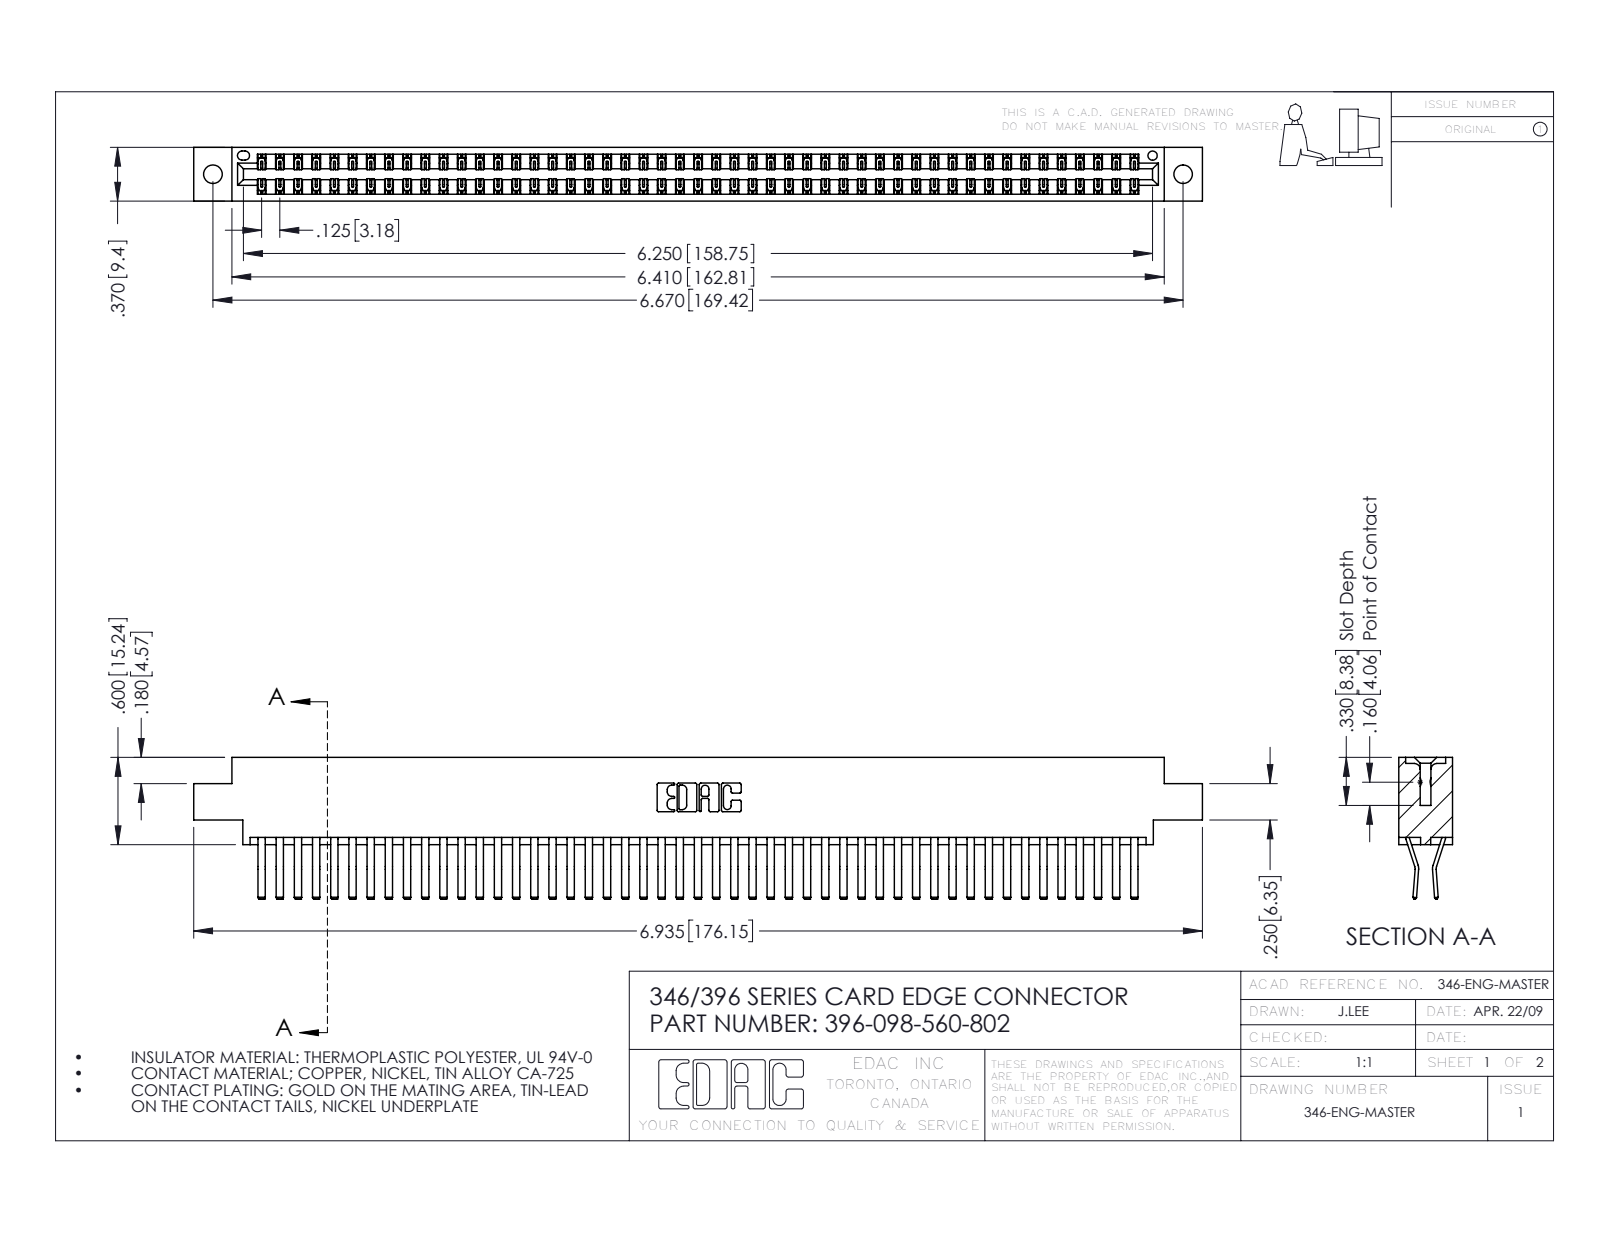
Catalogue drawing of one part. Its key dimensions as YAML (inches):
part_name: "346 Part_0.170 Offset - 0.128 Dia; 396-098-560-802; 345-292-001_560 Tail"
step_written_by: "SolidWorks 2016 (CONFIG_CONTROL_DESIGN)"
units: inches
bodies: {solids: 99, faces: 5418, planar: 3510, cylindrical: 1908, other: 0}
overall_size: [6.935, 0.975, 0.37]
volume: 1.079
surface_area: 40.36
round_holes:
  - {diameter: 0.128, count: 2}
  - {diameter: 0.064, count: 1}
partial_cylinders:
  - {radius: 0.006, count: 147}
  - {radius: 0.01, count: 22}
  - {radius: 0.007, count: 6}
  - {radius: 0.031, count: 6}
  - {radius: 0.026, count: 3}
  - {radius: 0.01, count: 2}
  - {radius: 0.014, count: 2}
  - {radius: 0.022, count: 2}
face_to_face_distances: [0.048, 0.322, 0.37, 0.025, 0.25, 0.072, 0.298, 0.275, 0.148, 0.222]
hole_center_spacings: [0.246, 6.461, 6.67]
